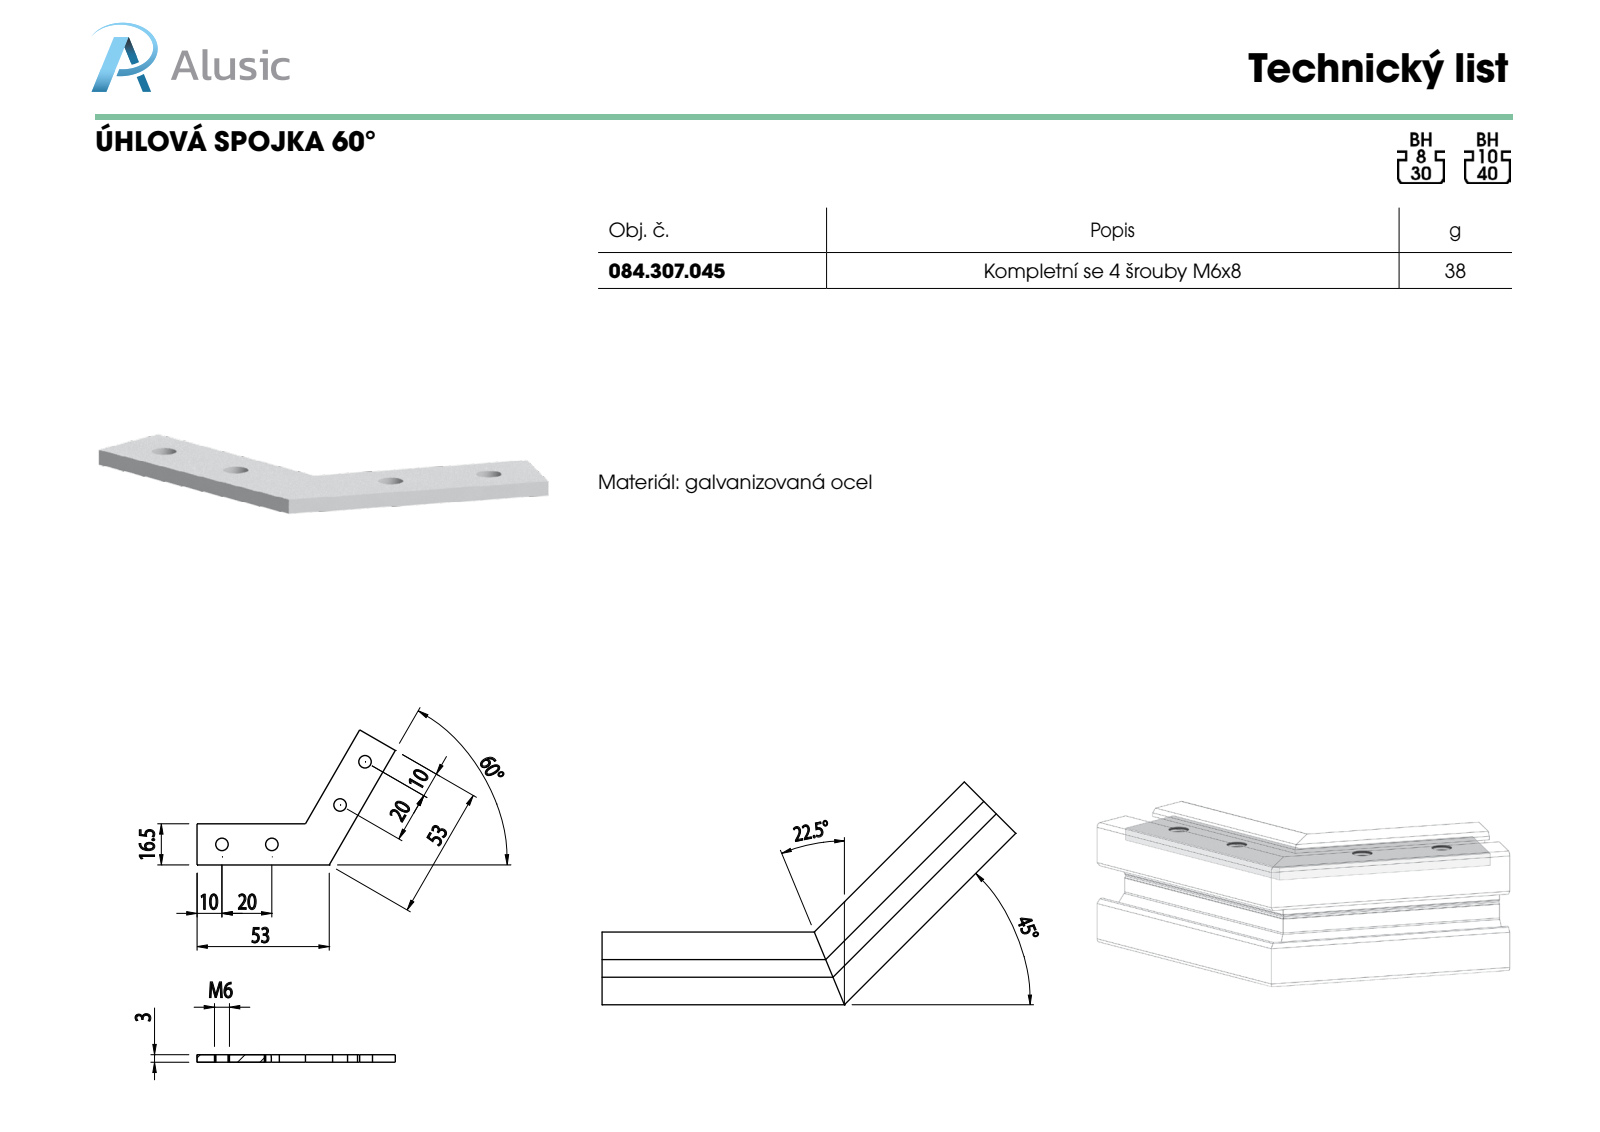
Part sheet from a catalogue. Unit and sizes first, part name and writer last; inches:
Units: inches
Overall size (bounding box): 3.13 × 2.132 × 0.118
Round holes (diameter × count): ⌀0.197 ×4
Main face-to-face distances: 0.118, 0.65
Hole centre spacings: 0.787, 1.965, 1.244, 2.607
Volume: 0.277 in³ · Surface area: 6.034 in²
Bodies: 1 solid, 16 faces (8 planar, 8 cylindrical, 0 other)
Part name (STEP PRODUCT): 084.307.045
STEP written by: SolidWorks 2012 (CONFIG_CONTROL_DESIGN)
